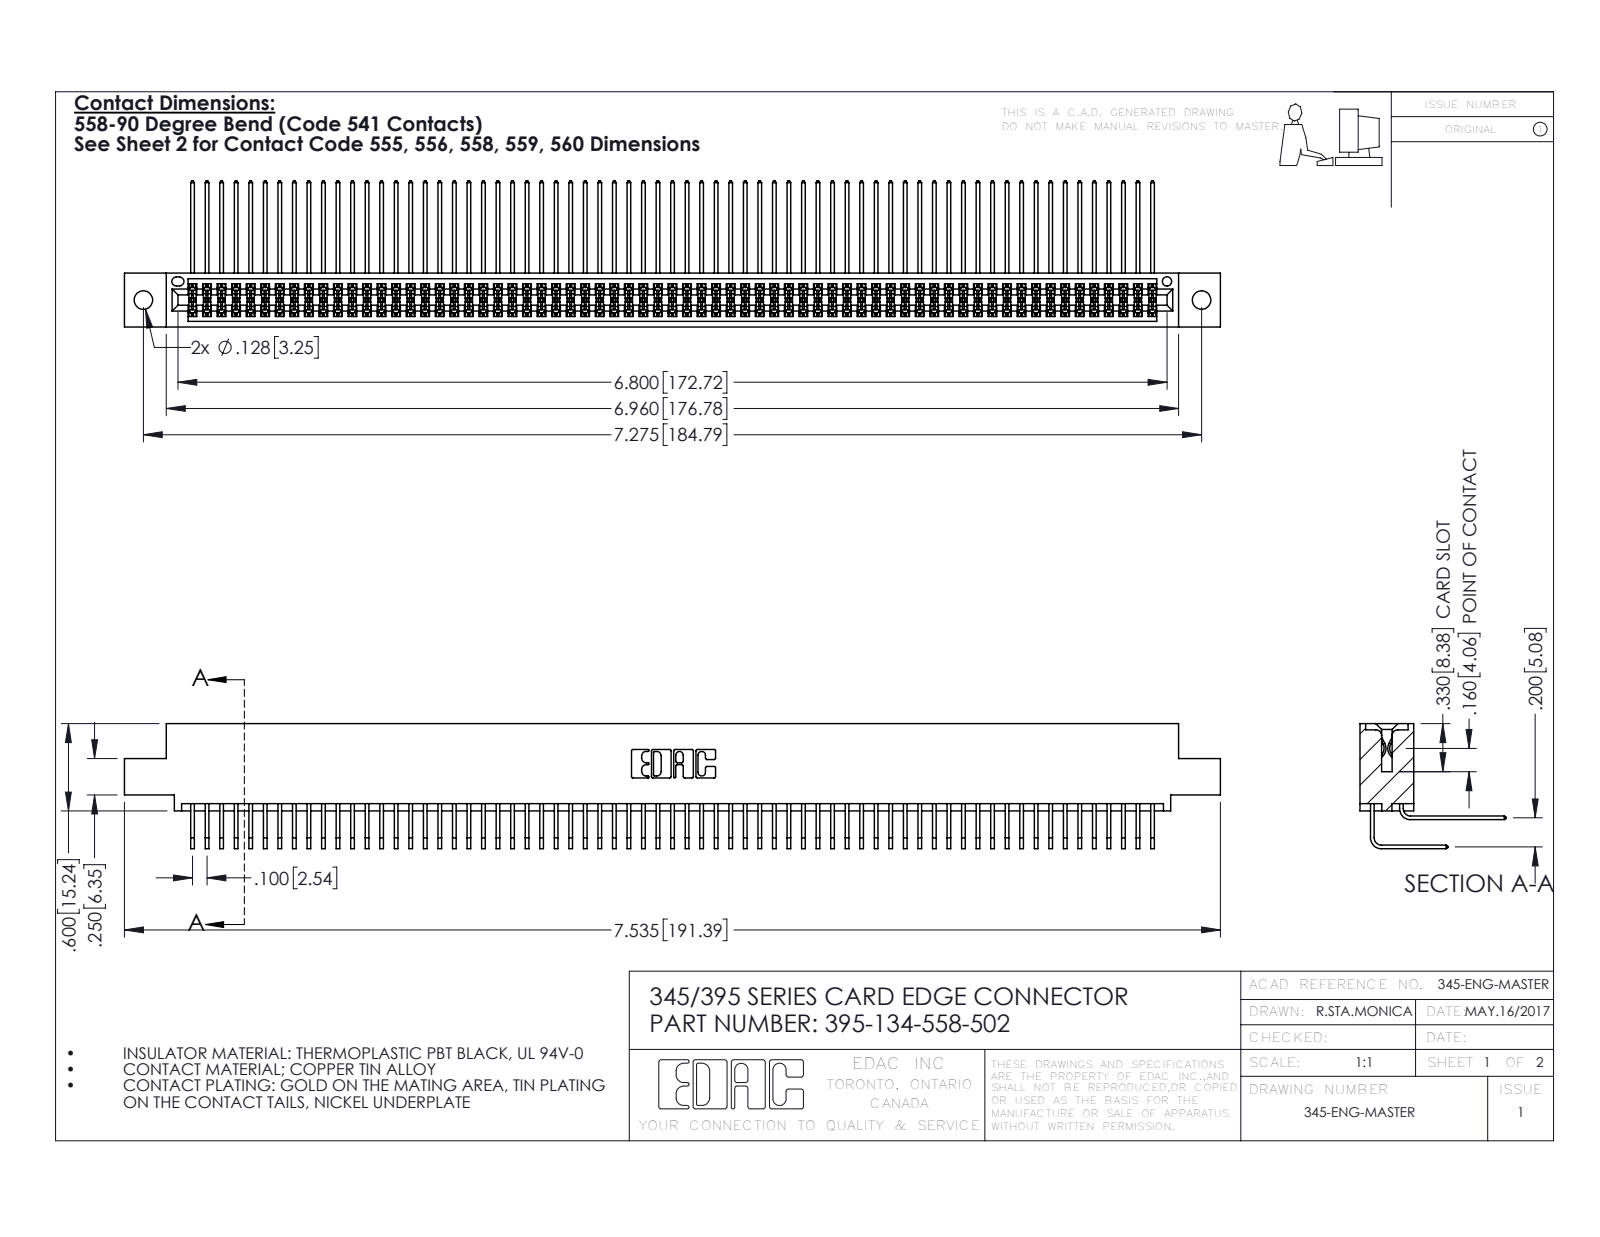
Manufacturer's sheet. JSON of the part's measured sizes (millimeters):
{"part_name": "345 Part_0.110 Offset - 0.128 Dia; 395-134-558-502; 345-292-001_558 Tail - 2; 345-292-001_558 559 Tail - 1", "step_written_by": "SolidWorks 2016 (CONFIG_CONTROL_DESIGN)", "units": "millimeters", "bodies": {"solids": 135, "faces": 7098, "planar": 4774, "cylindrical": 2324, "other": 0}, "overall_size": [191.4, 25.5, 21.8], "volume_mm3": 19480, "surface_area_mm2": 32740, "round_holes": [[3.3, 2], [1.6, 1]], "partial_cylinders_radius": [[0.2, 202], [0.3, 22], [0.2, 6], [0.8, 6], [0.7, 3], [0.4, 2], [0.5, 2], [0.6, 2]], "face_to_face_distances": [1.8, 7.6, 5.1, 9.4, 2.5, 6.9, 0.6, 5.7, 0.6, 4.4], "hole_center_spacings": [6.9, 178.8, 184.8]}
